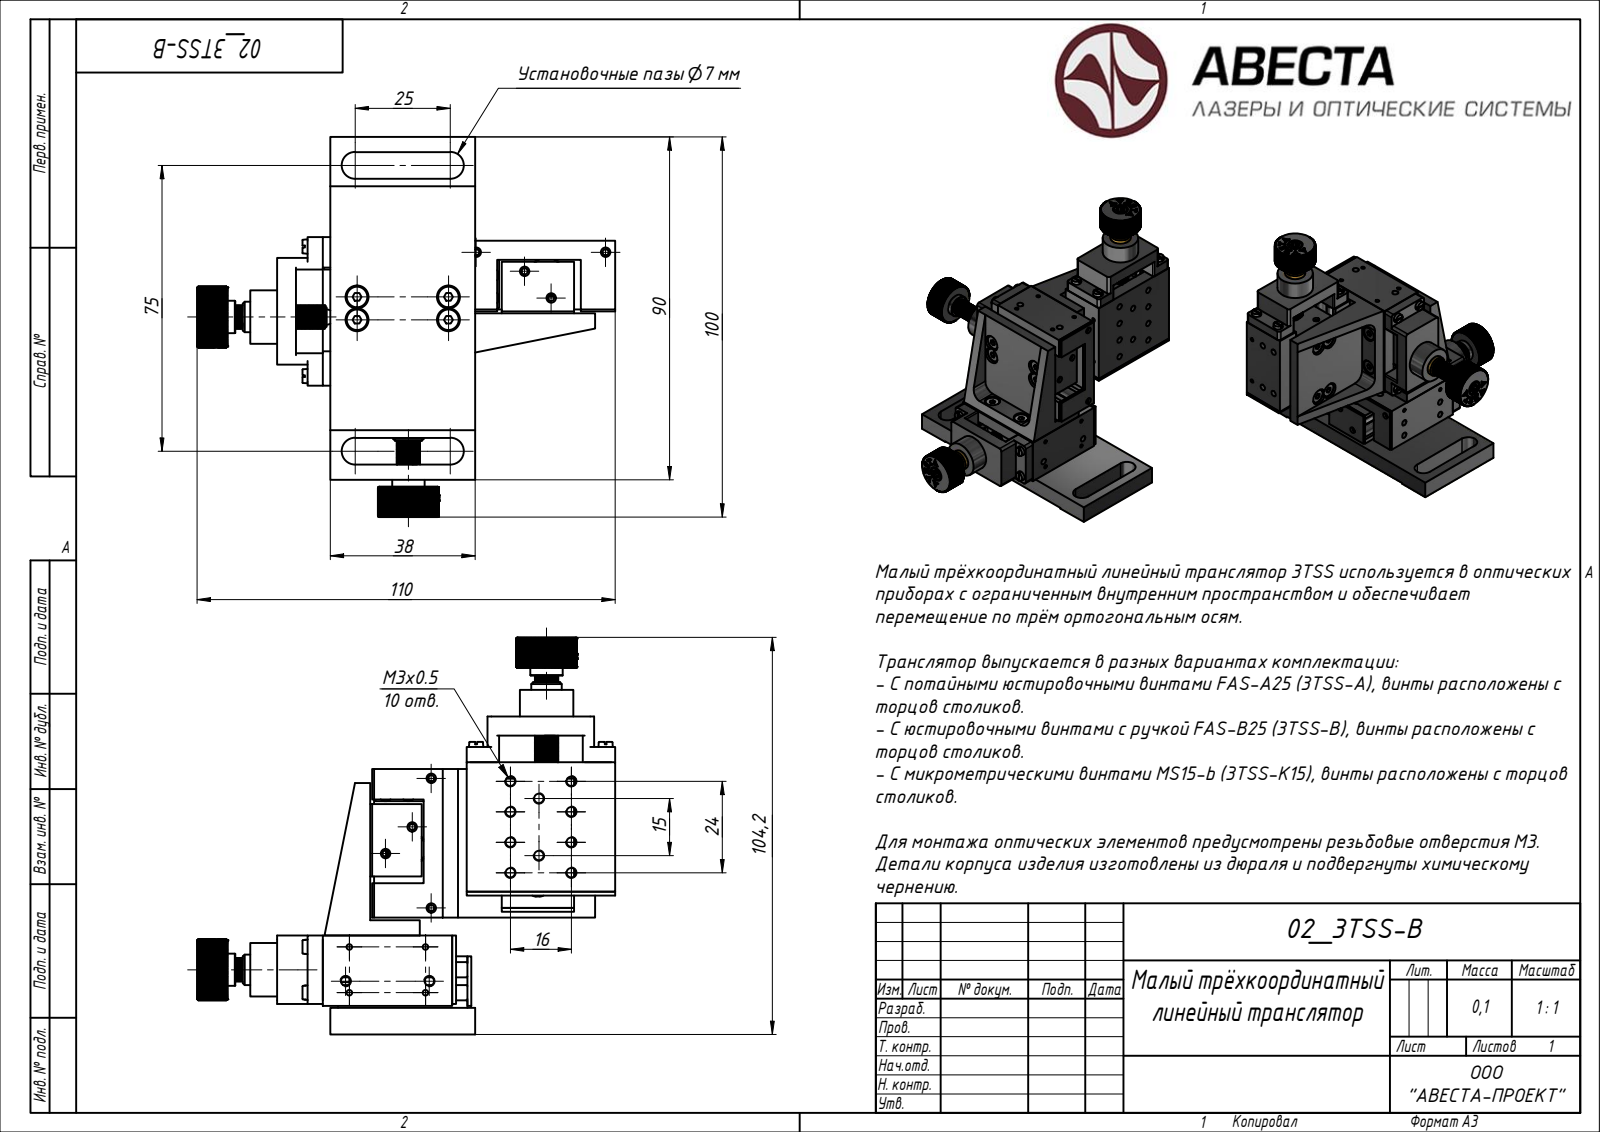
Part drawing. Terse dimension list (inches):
written by: Rhino 7.34 (AUTOMOTIVE_DESIGN)
unit: in
bodies: 10 solids, 3915 faces (2008 planar, 1207 cylindrical, 700 other)
size: 4.322 × 4.103 × 3.929
volume: 7.361 in³; area: 110.3 in²
holes: 37× ⌀0.097, 20× ⌀0.062, 18× ⌀0.097, 18× ⌀0.098, 16× ⌀0.134, 15× ⌀0.236, 12× ⌀0.059, 8× ⌀0.062, 8× ⌀0.256, 3× ⌀0.122, 3× ⌀0.374
bosses: 19× ⌀0.157, 12× ⌀0.218, 12× ⌀0.118, 4× ⌀0.211, 3× ⌀0.551, 3× ⌀0.354, 3× ⌀0.335, 3× ⌀0.315
rounds: 24× R0.039, 12× R0.02, 12× R0.079, 5× R0.031, 5× R0.048, 5× R0.048, 4× R0.031, 4× R0.138
face distances: 0.02, 0.079, 0.531, 0.059, 0.472, 0.453, 0.197, 0.748, 0.177, 1.043
hole spacings: 0.63, 0.236, 0.315, 0.835, 0.704, 0.124, 0.472, 0.822
